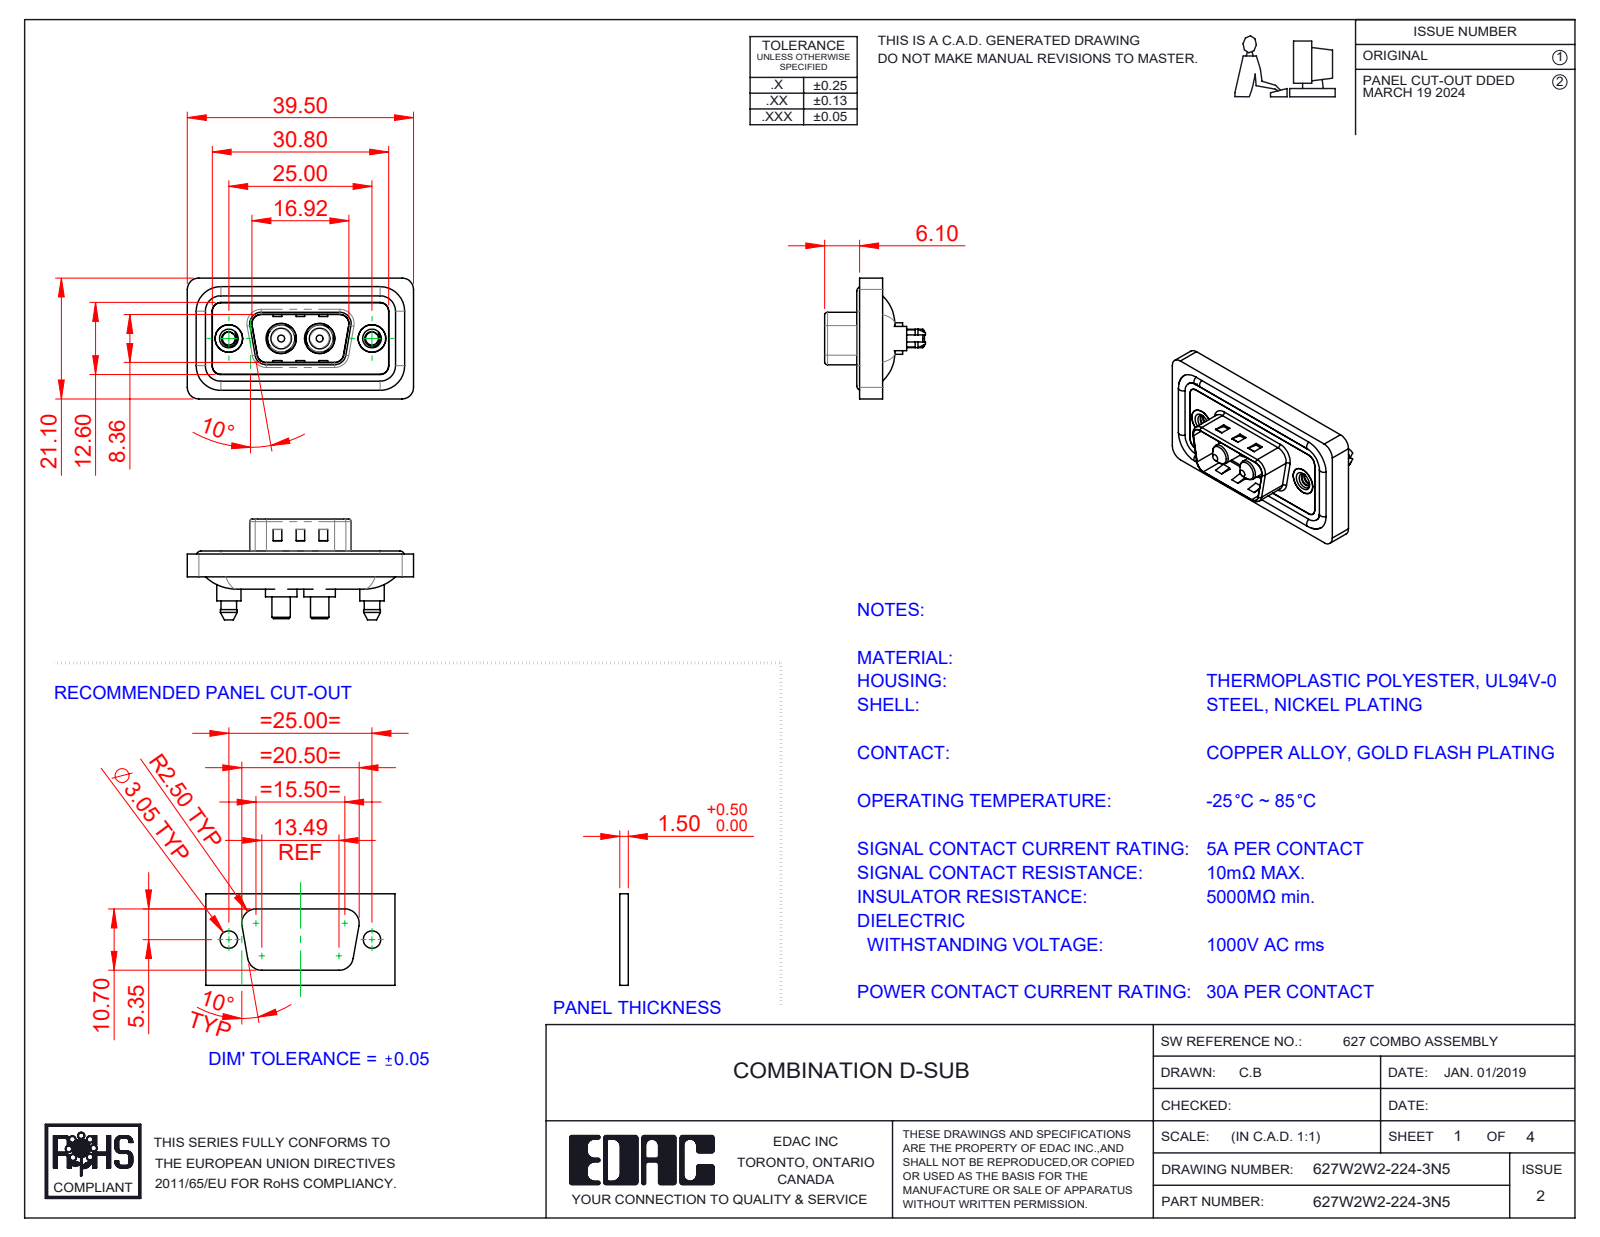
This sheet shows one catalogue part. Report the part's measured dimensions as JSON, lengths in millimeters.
{"part_name": "Power Pin_30A S; 627Combo Waterproof Housing_09 Contacts; 627Combo Threaded Boardlock_5; 627Combo Shell Rear_09 Contacts (+3 more)", "step_written_by": "SolidWorks 2023 (CONFIG_CONTROL_DESIGN)", "units": "millimeters", "bodies": {"solids": 11, "faces": 539, "planar": 181, "cylindrical": 250, "other": 108}, "overall_size": [39.5, 21.1, 17.6], "volume_mm3": 4608, "surface_area_mm2": 7326, "round_holes": [[2.26, 2], [4, 2], [4.8, 2], [4.85, 2], [5, 2], [5.3, 2]], "round_bosses_or_shafts": [[1.6, 4], [5.5, 2], [5.4, 2], [5.2, 2], [4.9, 2], [4.75, 2], [4.25, 2], [3.75, 2]], "partial_cylinders_radius": [[1.5, 24], [2, 18], [1.6, 10], [0.5, 8], [0.25, 4], [0.6, 4], [0.65, 4], [0.9, 4]], "face_to_face_distances": [0.4, 1.1, 2.9, 3.1, 0.5, 1.6, 1.5, 4, 0.7, 2.5], "hole_center_spacings": [9.14, 15.86, 6.72, 25]}
